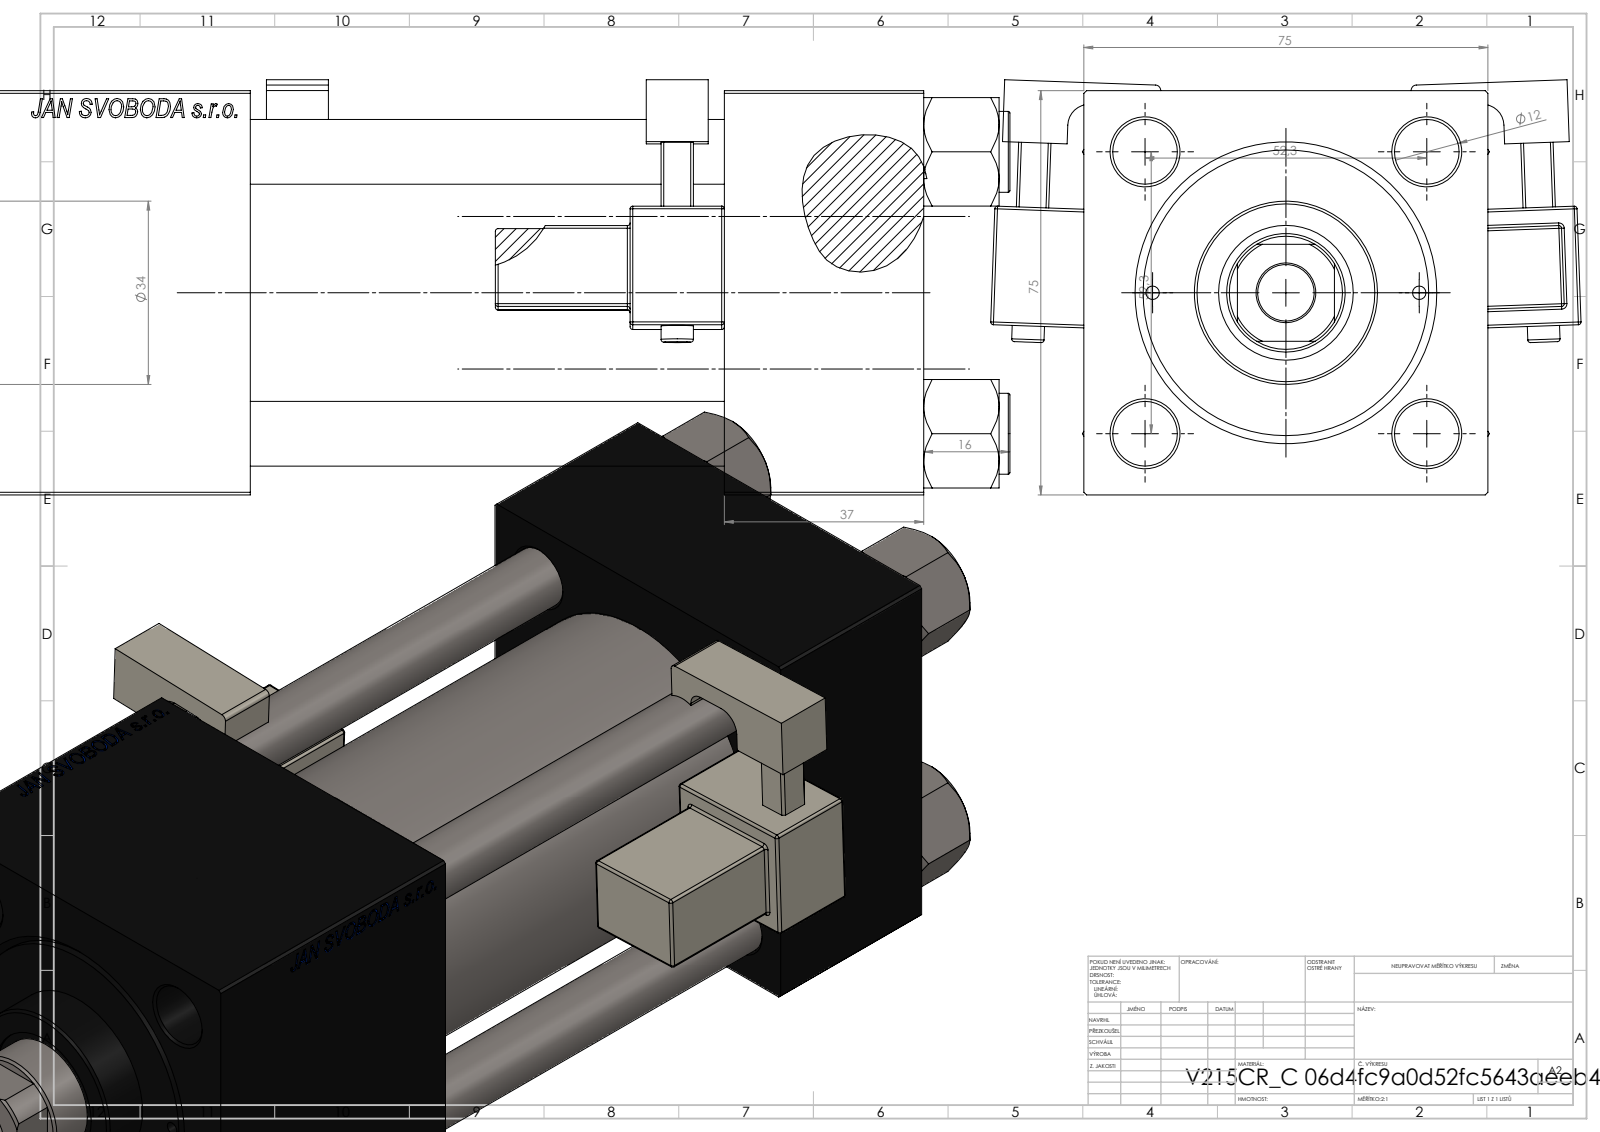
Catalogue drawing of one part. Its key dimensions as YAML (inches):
part_name: "NUT_M5_C; V215CR_C_TYCINKA; V215CR_MSU; V215CR_VCP_C (+2 more)"
step_written_by: "SolidWorks 2019 (CONFIG_CONTROL_DESIGN)"
units: inches
bodies: {solids: 13, faces: 1308, planar: 586, cylindrical: 150, other: 572}
overall_size: [8.858, 4.314, 3.033]
volume: 45.04
surface_area: 273.1
round_holes:
  - {diameter: 0.472, count: 4}
  - {diameter: 0.098, count: 2}
  - {diameter: 0.276, count: 2}
  - {diameter: 0.825, count: 2}
  - {diameter: 1.181, count: 2}
  - {diameter: 0.413, count: 1}
  - {diameter: 0.866, count: 1}
  - {diameter: 0.984, count: 1}
  - {diameter: 1.614, count: 1}
  - {diameter: 1.969, count: 1}
  - {diameter: 2.087, count: 1}
round_bosses_or_shafts:
  - {diameter: 0.591, count: 4}
  - {diameter: 0.236, count: 2}
  - {diameter: 2.205, count: 1}
  - {diameter: 1.339, count: 1}
partial_cylinders:
  - {radius: 0.02, count: 48}
  - {radius: 0.039, count: 2}
  - {radius: 0.098, count: 2}
  - {radius: 0.157, count: 2}
  - {radius: 0.413, count: 1}
face_to_face_distances: [2.953, 1.457, 2.323, 7.244, 5.787, 4.921, 3.465, 6.114, 4.657, 1.193]
hole_center_spacings: [1.031, 1.456, 2.059, 2.253, 0.974, 2.912, 1.949, 4.862]
